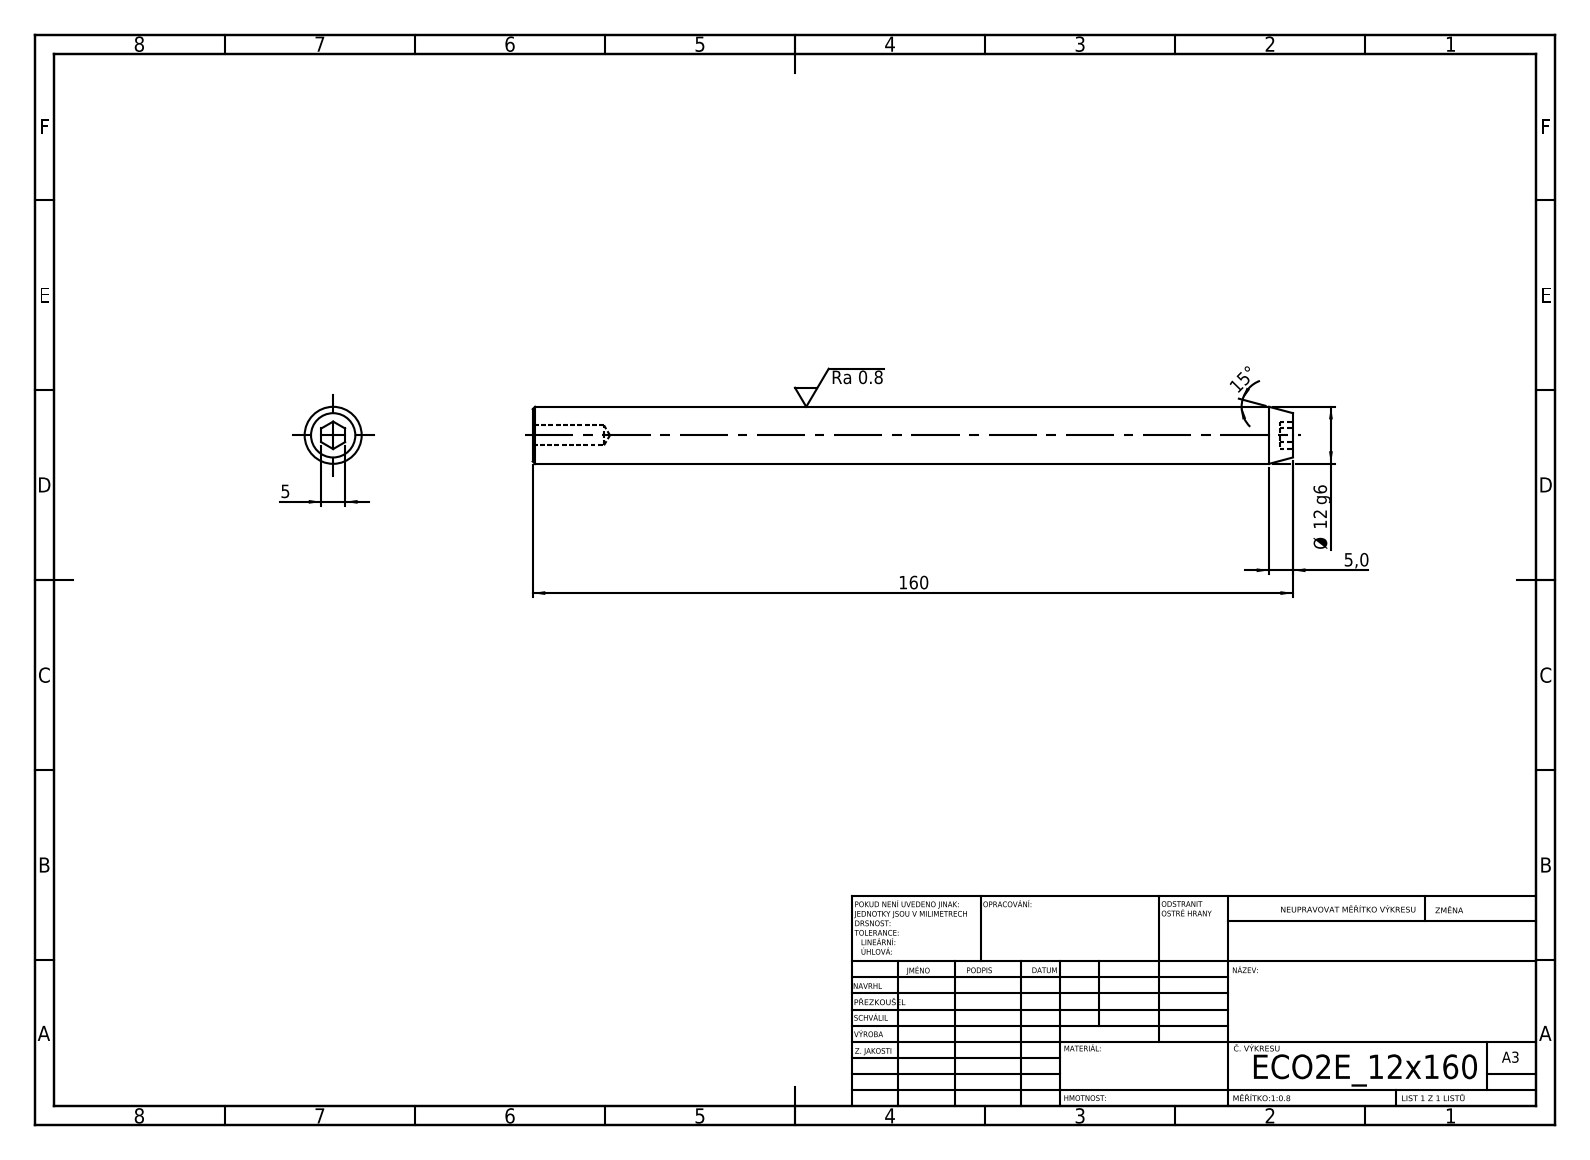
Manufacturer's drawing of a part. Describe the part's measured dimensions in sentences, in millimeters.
Its 3-D file was written by "SolidWorks 2019 (CONFIG_CONTROL_DESIGN)". It is 1 solid with 19 faces: 9 planar, 4 cylindrical and 6 other. Overall it measures 160 by 12 by 12 millimeters. Its volume is 17 700 cubic millimeters and its surface area 6 435 square millimeters. Round holes: 1 of diameter 4.2. Round bosses or shafts: 1 of diameter 12. The main face-to-face distances are 160, 5, 2.8, 157.2.
